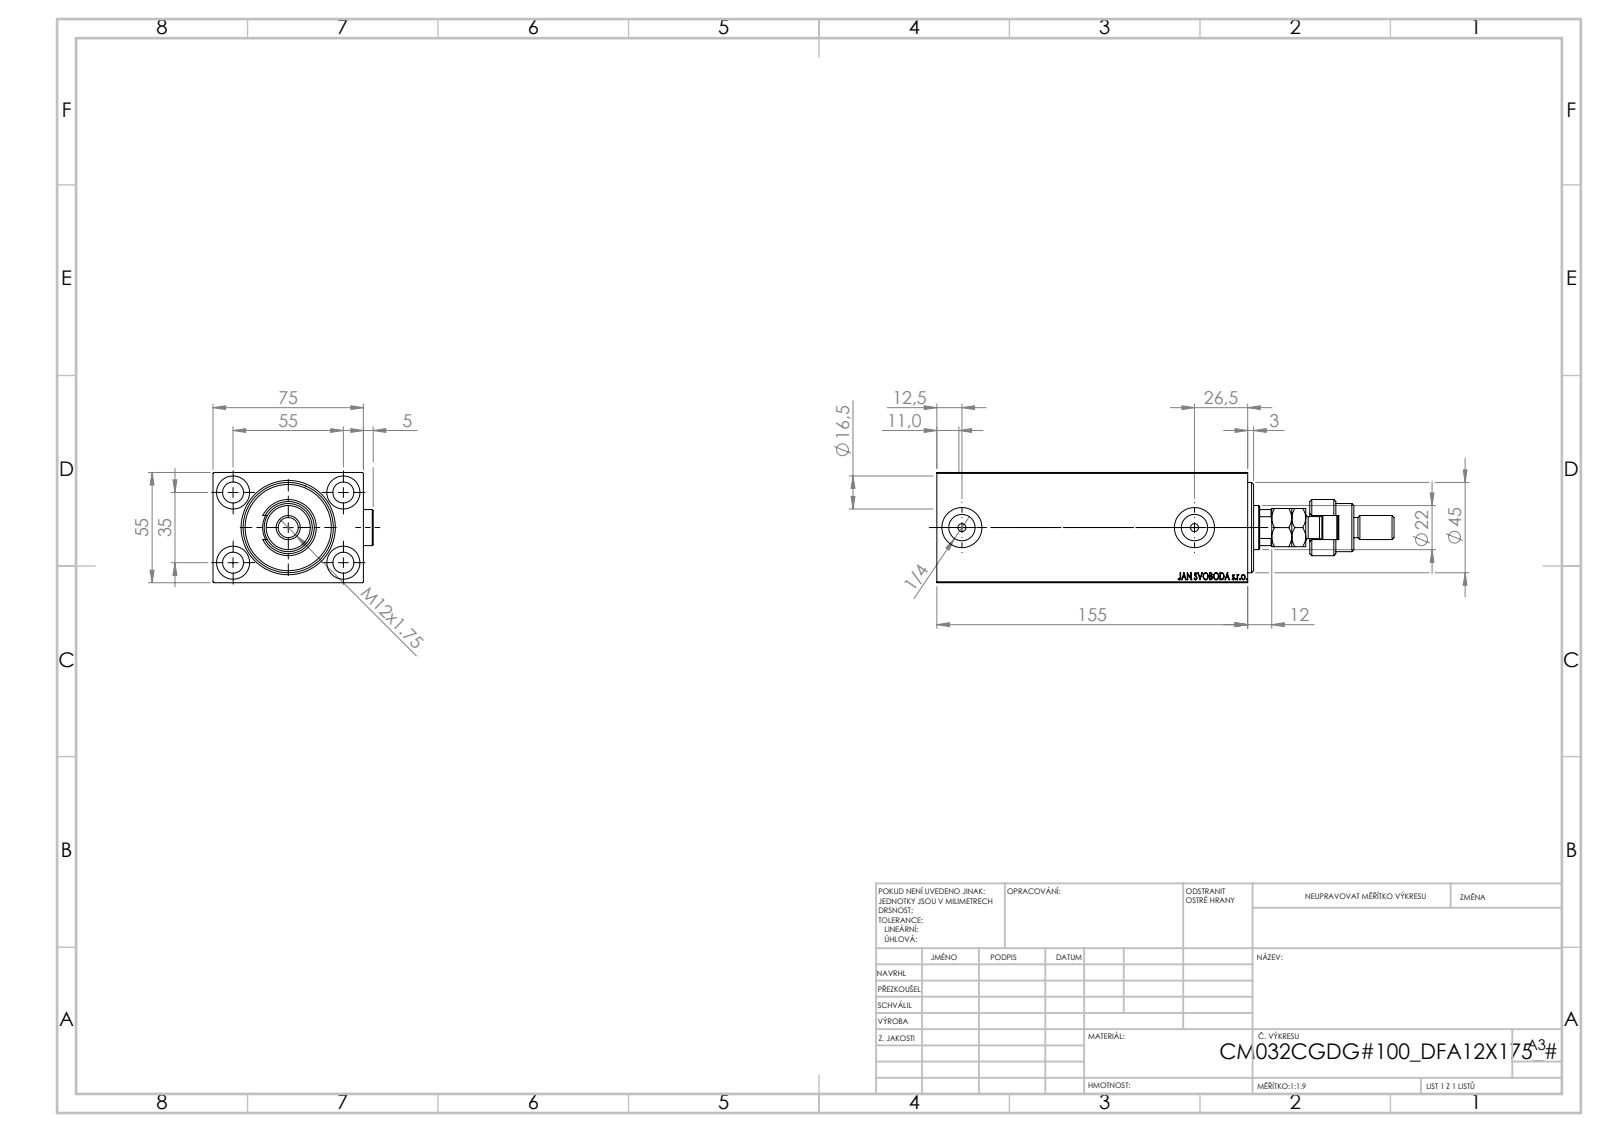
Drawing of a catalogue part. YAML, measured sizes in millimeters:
part_name: "V450CM_VC_B; V450CM_C_Body; V450CM_C_VCP; Zatka_OIL_PORT (+2 more)"
step_written_by: "SolidWorks 2019 (CONFIG_CONTROL_DESIGN)"
units: millimeters
bodies: {solids: 7, faces: 1001, planar: 470, cylindrical: 89, other: 442}
overall_size: [228, 79.9, 55]
volume: 550377
surface_area: 115245
round_holes:
  - {diameter: 10.5, count: 5}
  - {diameter: 16.5, count: 4}
  - {diameter: 4, count: 2}
  - {diameter: 13.16, count: 2}
  - {diameter: 20, count: 2}
  - {diameter: 22, count: 1}
  - {diameter: 25.5, count: 1}
  - {diameter: 32, count: 1}
  - {diameter: 34, count: 1}
  - {diameter: 45, count: 1}
round_bosses_or_shafts:
  - {diameter: 18, count: 3}
  - {diameter: 28, count: 1}
  - {diameter: 24, count: 1}
  - {diameter: 12, count: 1}
  - {diameter: 11, count: 1}
  - {diameter: 10, count: 1}
partial_cylinders:
  - {radius: 9.75, count: 1}
  - {radius: 10.5, count: 1}
face_to_face_distances: [55, 75, 5, 10, 145, 155, 8, 150, 140, 74.9]
hole_center_spacings: [32.6, 35, 55, 65.19, 116]
